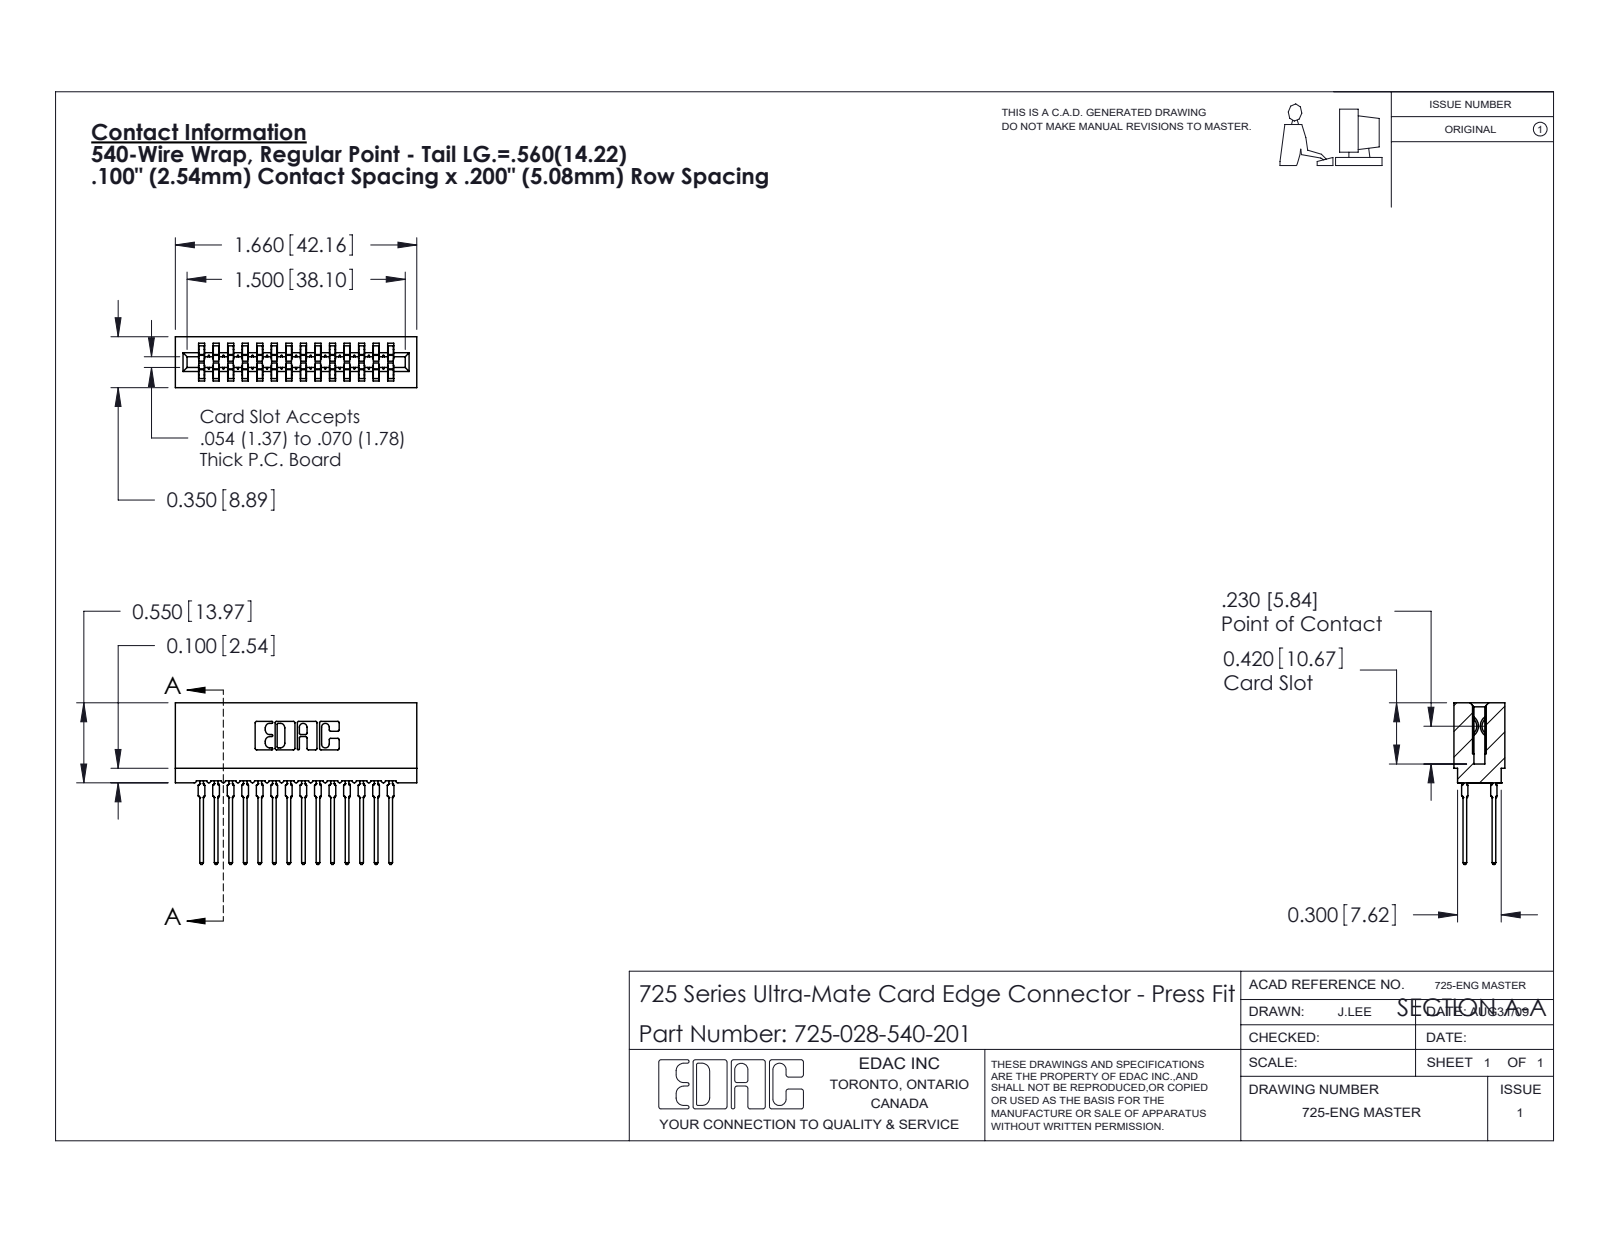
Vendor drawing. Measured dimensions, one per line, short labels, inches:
name: 725-028-540-201; 745-292-001_540; 725 Part_Insulator Option - 01
written by: SolidWorks 2020 (CONFIG_CONTROL_DESIGN)
unit: in
bodies: 29 solids, 2601 faces (1343 planar, 530 cylindrical, 728 other)
size: 1.66 × 1.111 × 0.35
volume: 0.218 in³; area: 11.26 in²
rounds: 56× R0.021, 28× R0.015, 22× R0.01, 8× R0.005, 8× R0.011, 6× R0.007, 6× R0.031, 3× R0.026
face distances: 0.2, 0.1, 0.3, 0.6, 0.063, 0.287, 0.4, 0.5, 0.7, 0.35
